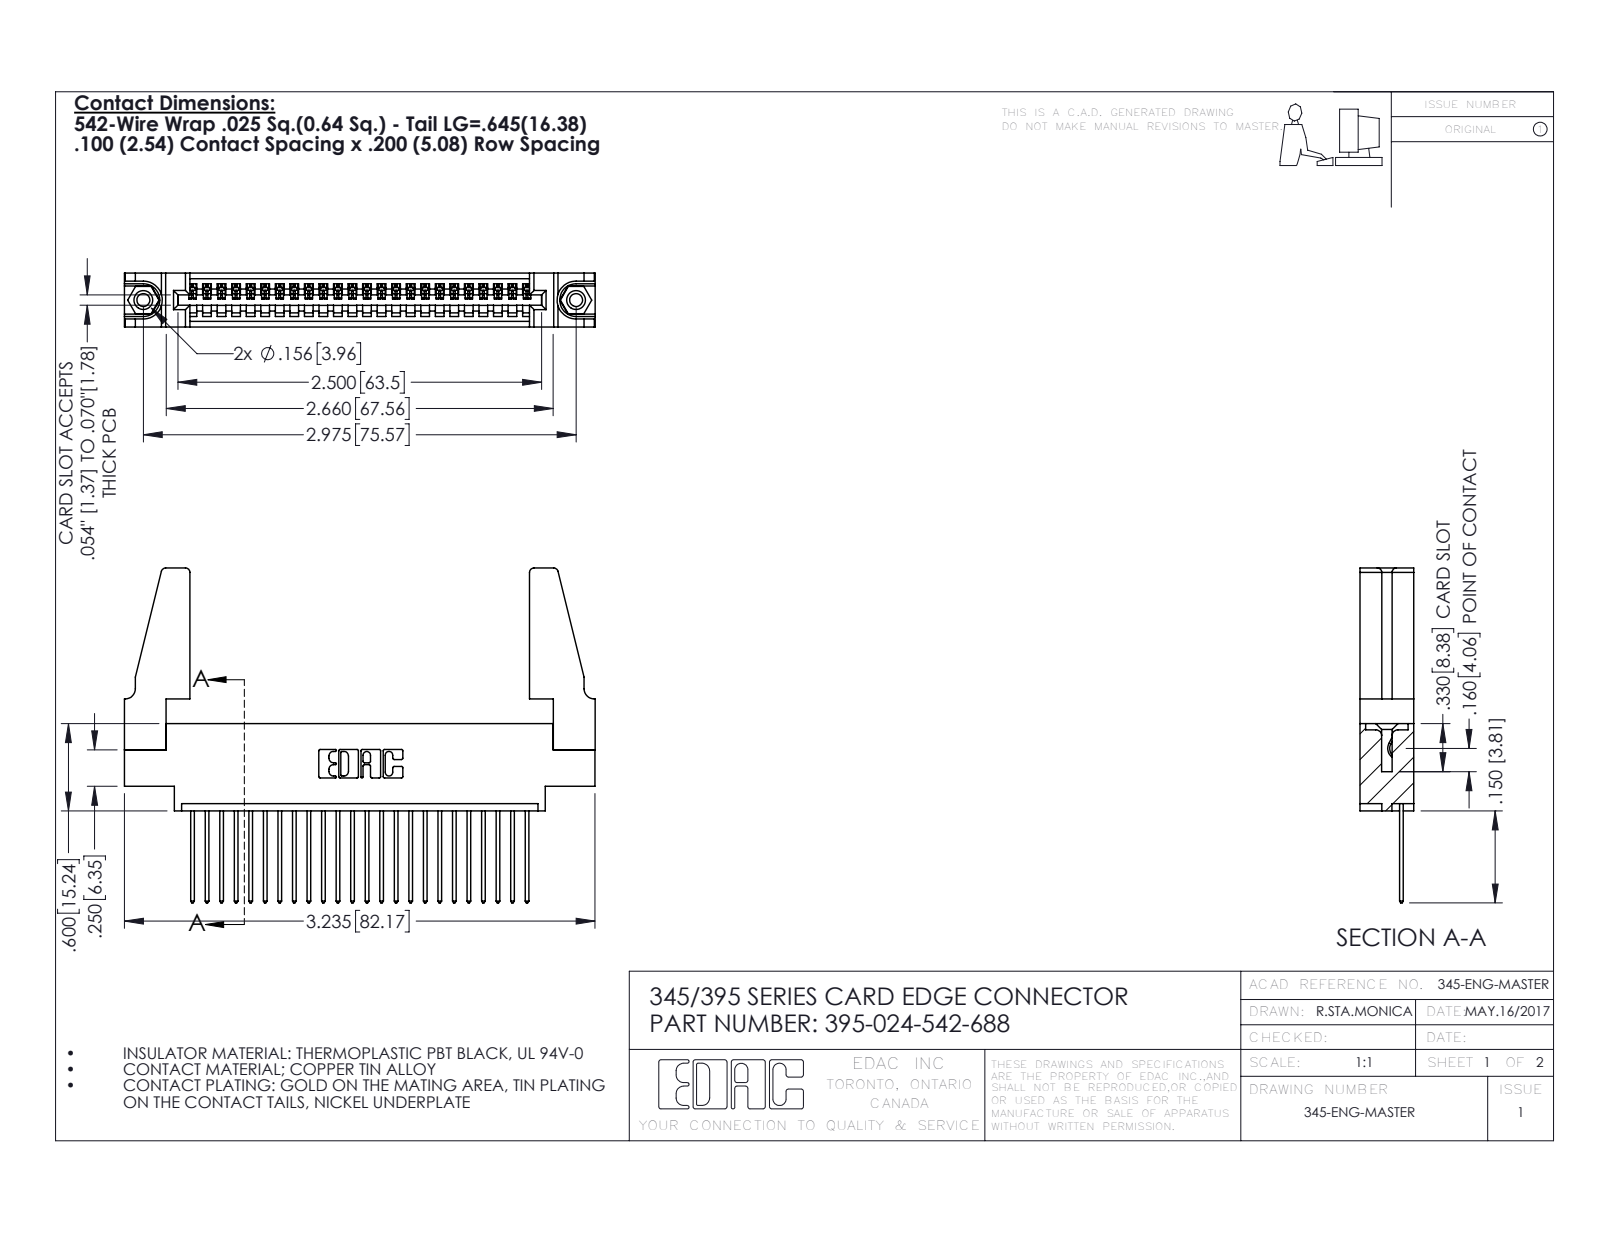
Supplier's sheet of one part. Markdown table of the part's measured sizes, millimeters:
| quantity | value |
| --- | --- |
| part name | 395-024-542-688; 345 Part_0.170 Offset - 0.156 Dia-TH; 345-250-001_345-250-001-102; 345-220-078_345-220-088 (+1 more) |
| STEP written by | SolidWorks 2016 (CONFIG_CONTROL_DESIGN) |
| units | millimeters |
| bodies | 29 solids, 1646 faces (1116 planar, 514 cylindrical, 16 other) |
| overall size | 82.2 × 58.5 × 9.4 |
| volume | 10 800 mm³ |
| surface area | 13 450 mm² |
| round holes (diameter × count) | 2.3 × 2, 3.2 × 2, 4 × 2, 1.6 × 1 |
| round bosses / shafts (diameter × count) | 3.9 × 2 |
| partial cylindrical surfaces (radius × count) | 0.2 × 48, 0.3 × 48, 0.3 × 22, 0.8 × 8, 0.2 × 6, 0.8 × 6, 0.7 × 3, 0.8 × 2 |
| main face-to-face distances | 9.4, 1.8, 7.6, 2.5, 6.9, 0.6, 5.1, 5.7, 4.4, 3.8 |
| hole center spacings | 6.9, 69.6, 75.6 |
